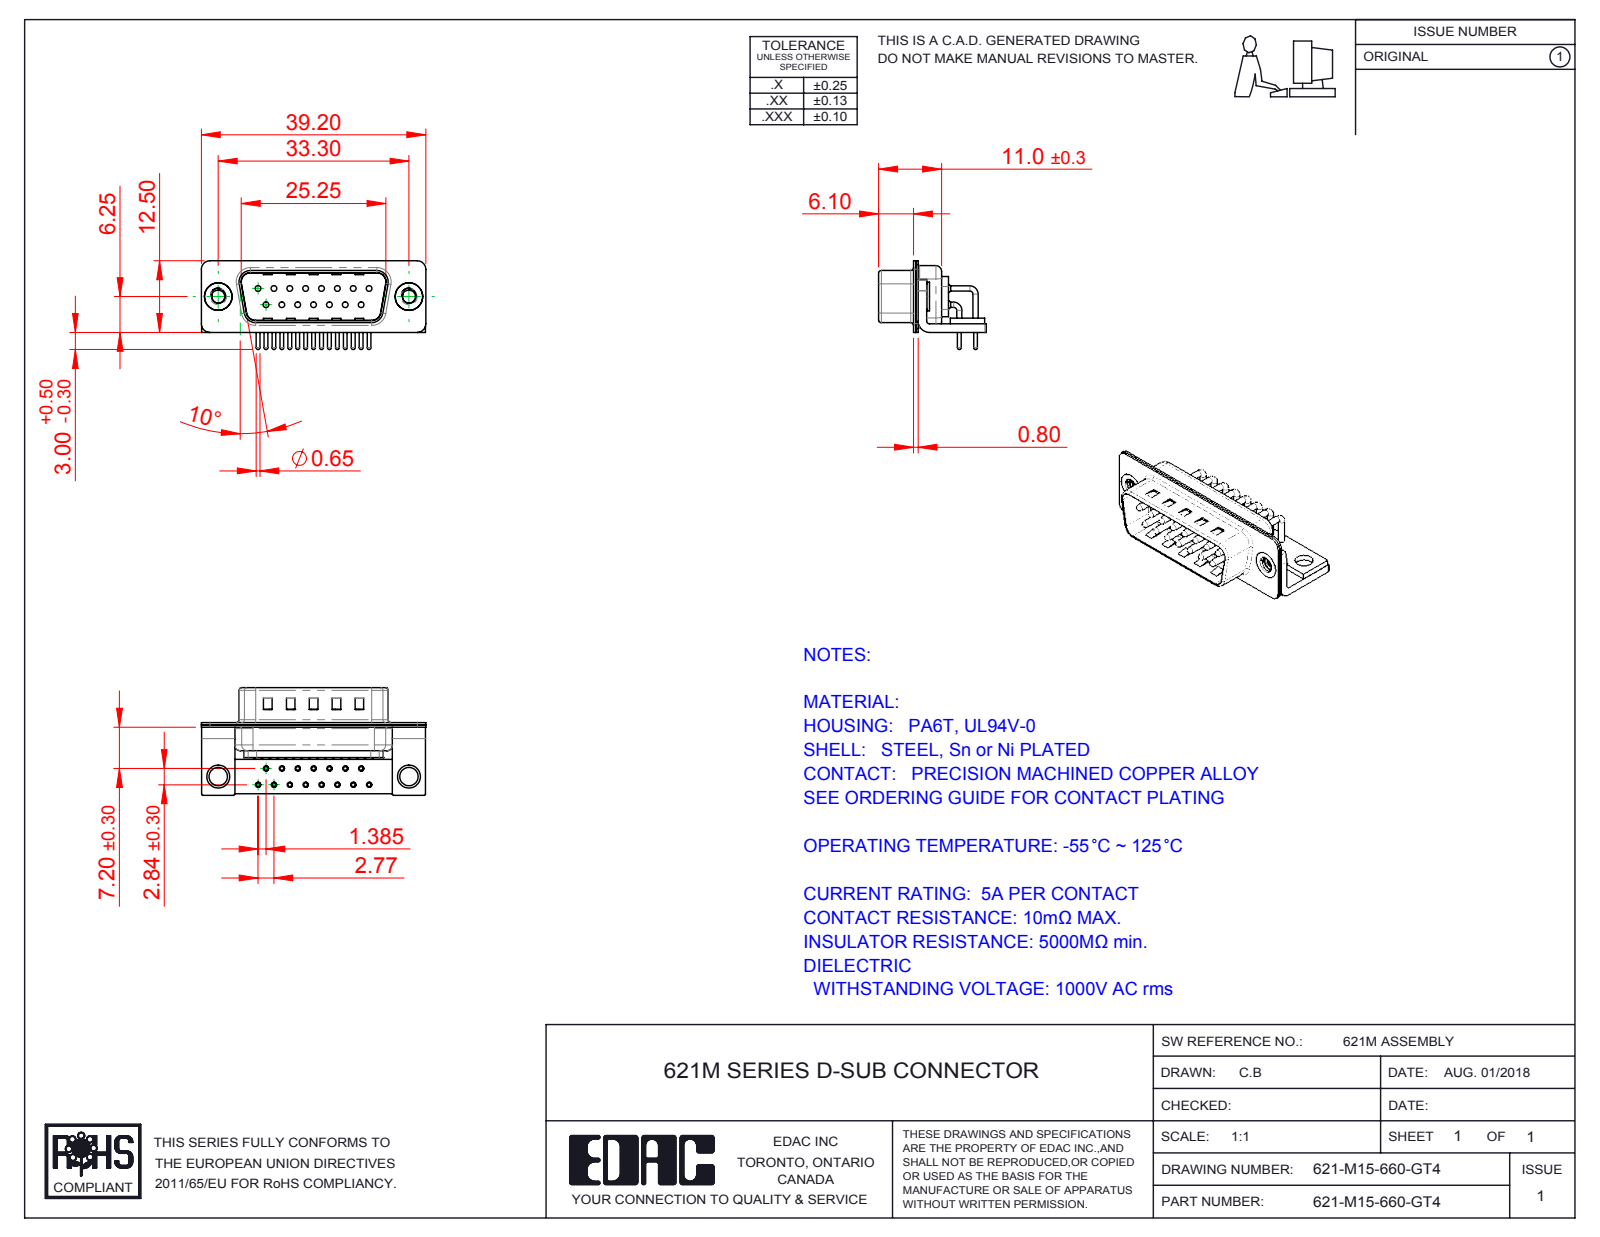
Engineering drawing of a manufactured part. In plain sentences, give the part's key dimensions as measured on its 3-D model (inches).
The part is named "621M Stabilizer Board_15 Contacts; 621M Housing_15 Contacts; 621M 4-40 Threaded Rivet_Stabilizer; 621-M15-660-GT4 (+5 more)". Its 3-D file was written by "SolidWorks 2016 (CONFIG_CONTROL_DESIGN)". It is 23 solids with 2070 faces: 1125 planar, 725 cylindrical and 220 other. Overall it measures 1.543 by 0.74 by 0.61 inches. Its volume is 0.145 cubic inches and its surface area 9.841 square inches. Round holes: 15 of diameter 0.035, 15 of diameter 0.039, 15 of diameter 0.067, 15 of diameter 0.079, 2 of diameter 0.089, 2 of diameter 0.126, 2 of diameter 0.157, 2 of diameter 0.189. Round bosses or shafts: 22 of diameter 0.035, 15 of diameter 0.059, 15 of diameter 0.026, 2 of diameter 0.197, 2 of diameter 0.193. Partial cylindrical surfaces (rounded edges, fillets, slot ends): 16 of radius 0.01, 16 of radius 0.059, 15 of radius 0.04, 13 of radius 0.079, 9 of radius 0.02, 8 of radius 0.063, 4 of radius 0.024, 4 of radius 0.026. The main face-to-face distances are 0.016, 0.033, 0.059, 0.031, 0.049, 0.409, 0.376, 0.039, 0.083, 0.075. The hole center spacings are 0.124, 0.109, 0.218, 0.327, 0.436, 0.198, 0.198, 0.294.
